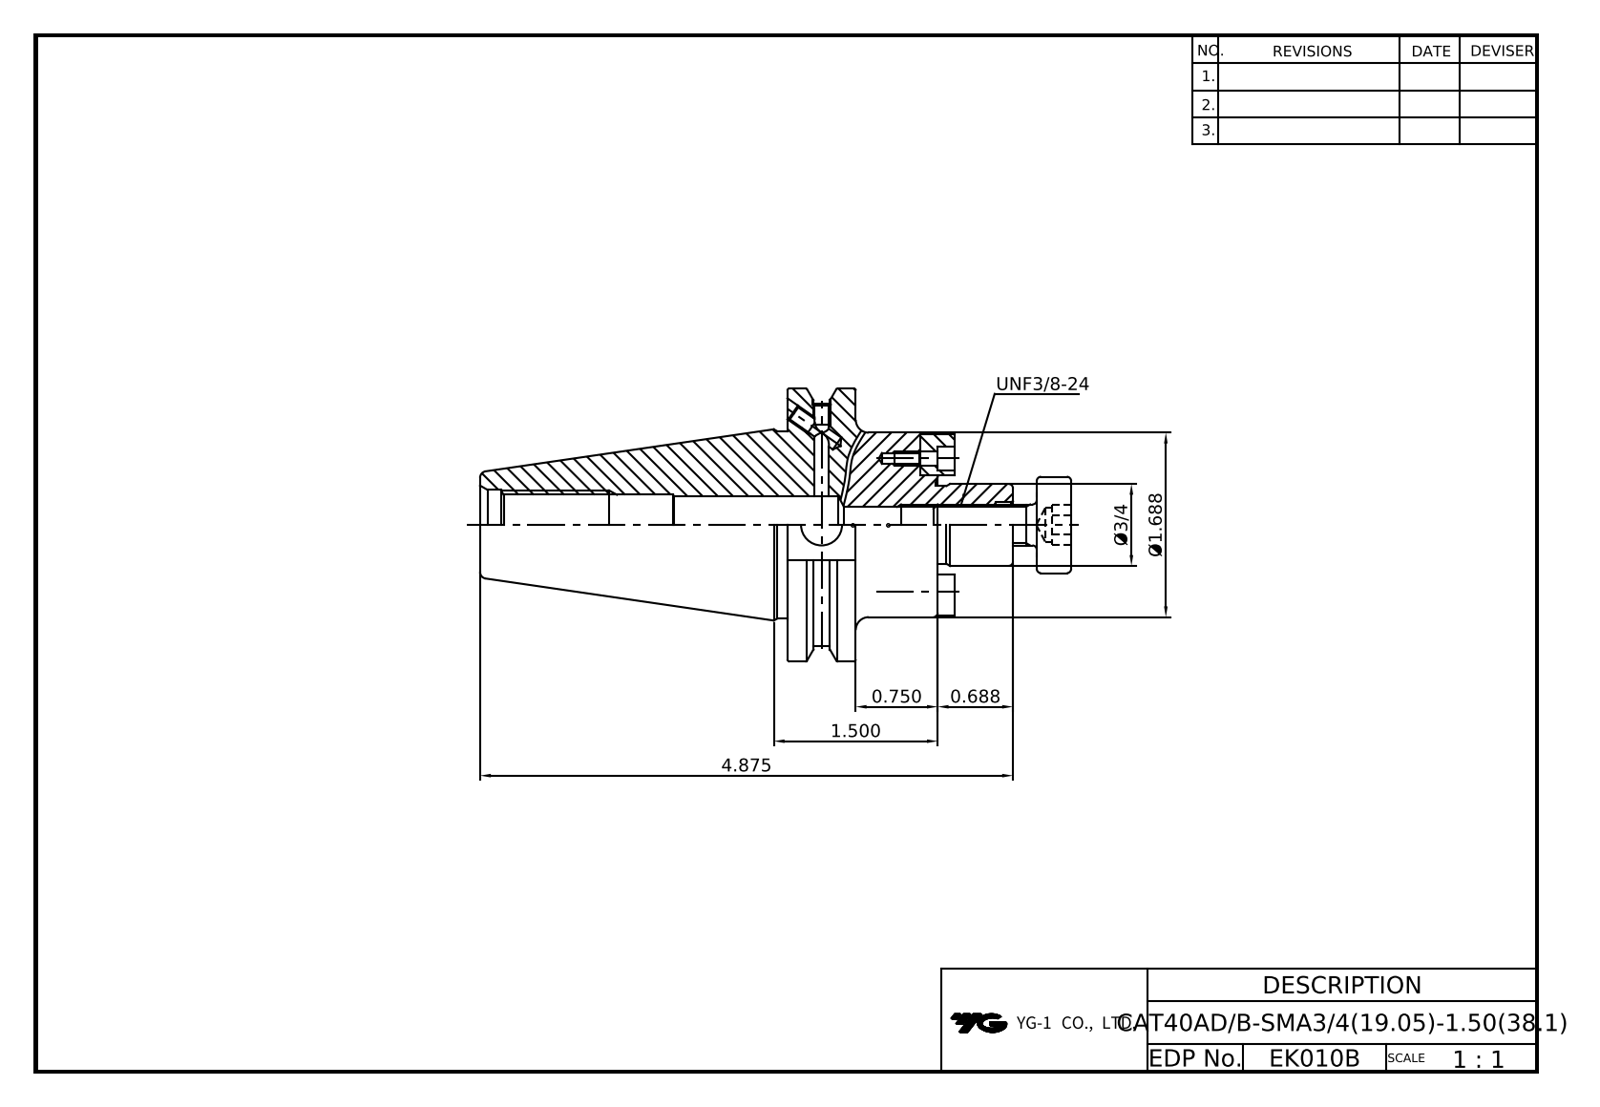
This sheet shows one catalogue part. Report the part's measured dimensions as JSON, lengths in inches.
{"part_name": "EK010B-CAT40ADB-SMA0_75-1_5; SMA19_05_DRIVE_KEY; SMA19_05_COLLAR_BOLT; EK010B-CAT40ADB-SMA0_75-1_5_ASM", "step_written_by": "PRO/ENGINEER BY PARAMETRIC TECHNOLOGY CORPORATION, 2012130 (CONFIG_CONTROL_DESIGN)", "units": "inches", "bodies": {"solids": 4, "faces": 245, "planar": 85, "cylindrical": 90, "other": 70}, "overall_size": [5.407, 2.5, 2.395], "volume_in3": 8.285, "surface_area_in2": 49.45, "round_holes": [[0.13, 5], [0.157, 3], [0.101, 2], [0.125, 2], [0.213, 2], [0.375, 2], [0.165, 1], [0.313, 1], [0.332, 1], [0.413, 1], [0.531, 1], [0.625, 1]], "round_bosses_or_shafts": [[2.5, 1], [1.717, 1], [1.688, 1], [0.882, 1], [0.75, 1], [0.726, 1], [0.375, 1], [0.332, 1]], "partial_cylinders_radius": [[0.155, 2], [0.156, 2], [1.108, 1]], "face_to_face_distances": [0.626, 1.375, 0.749, 1.969, 2.595, 1.22, 1.219, 0.593, 0.156, 1.376], "hole_center_spacings": [0.609, 1.218]}
